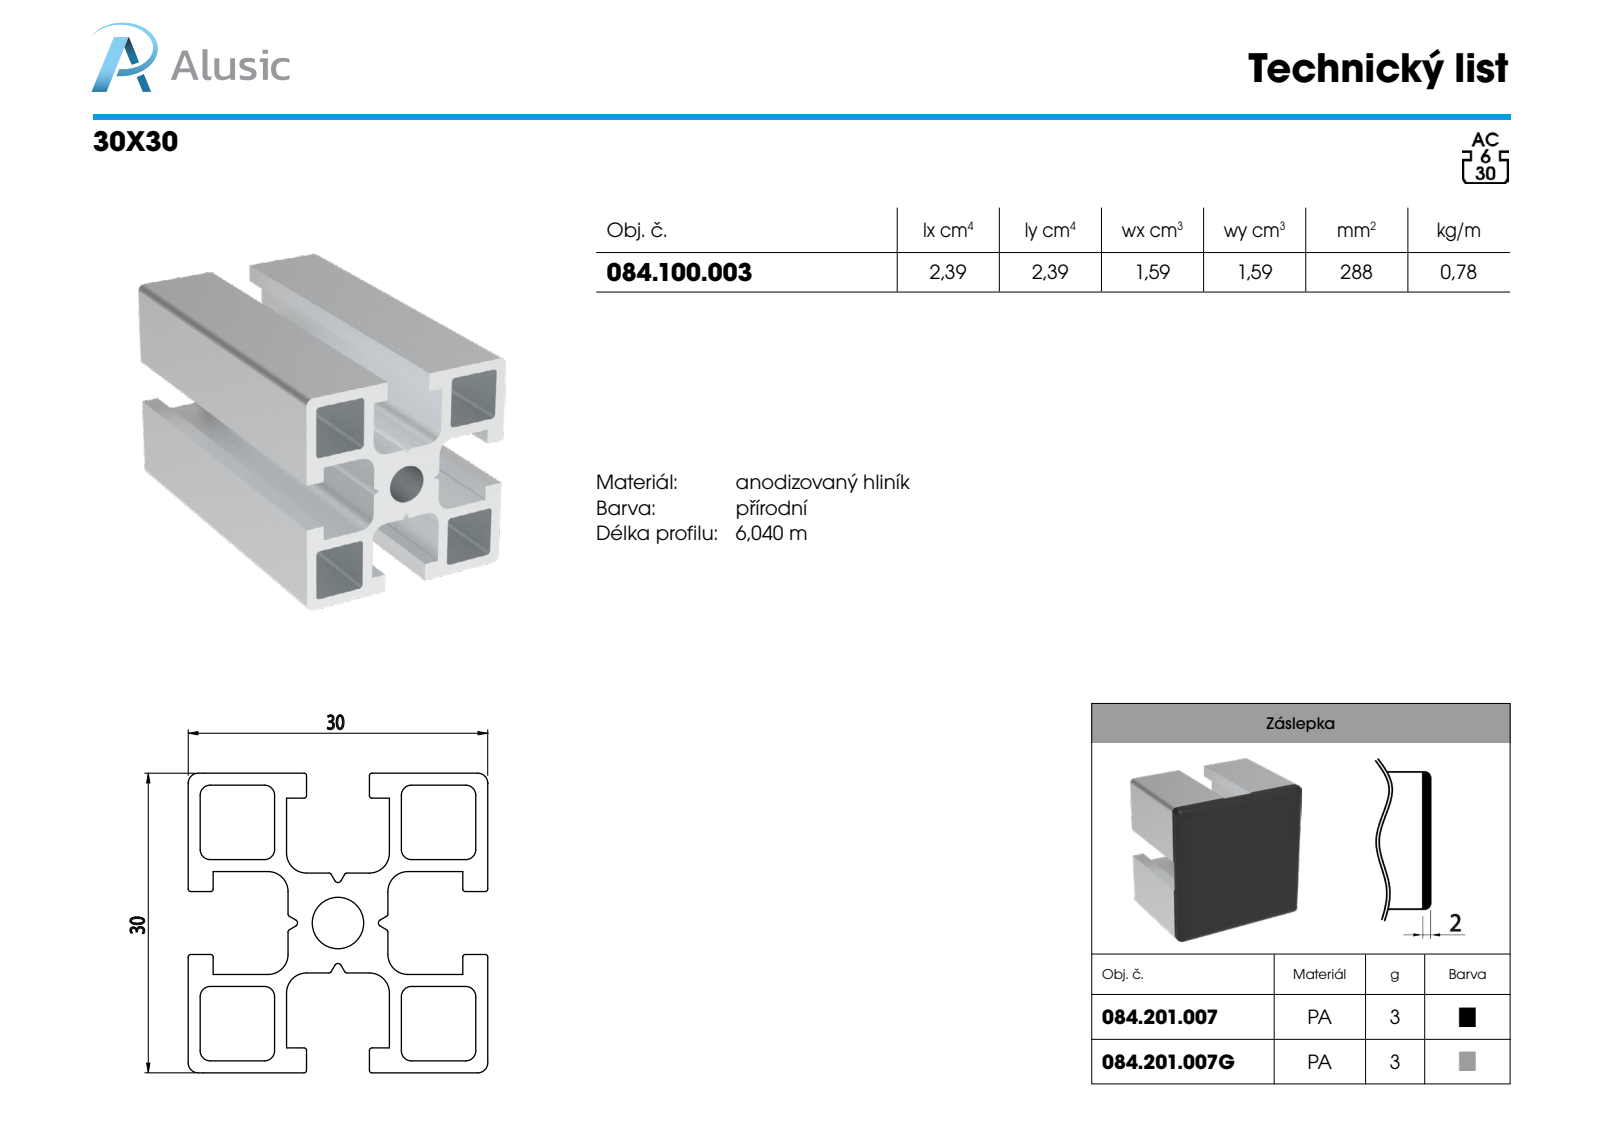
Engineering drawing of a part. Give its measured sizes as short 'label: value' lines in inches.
name: 084.100.003
written by: SolidWorks 2011 (CONFIG_CONTROL_DESIGN)
unit: in
bodies: 1 solid, 96 faces (66 planar, 30 cylindrical, 0 other)
size: 3.937 × 1.181 × 1.181
volume: 1.932 in³; area: 55.52 in²
holes: 1× ⌀0.203
rounds: 16× R0.02, 8× R0.079, 4× R0.039
face distances: 0.055, 1.126, 0.331, 0.85, 0.795, 0.276, 0.388, 0.793, 0.333, 0.738
